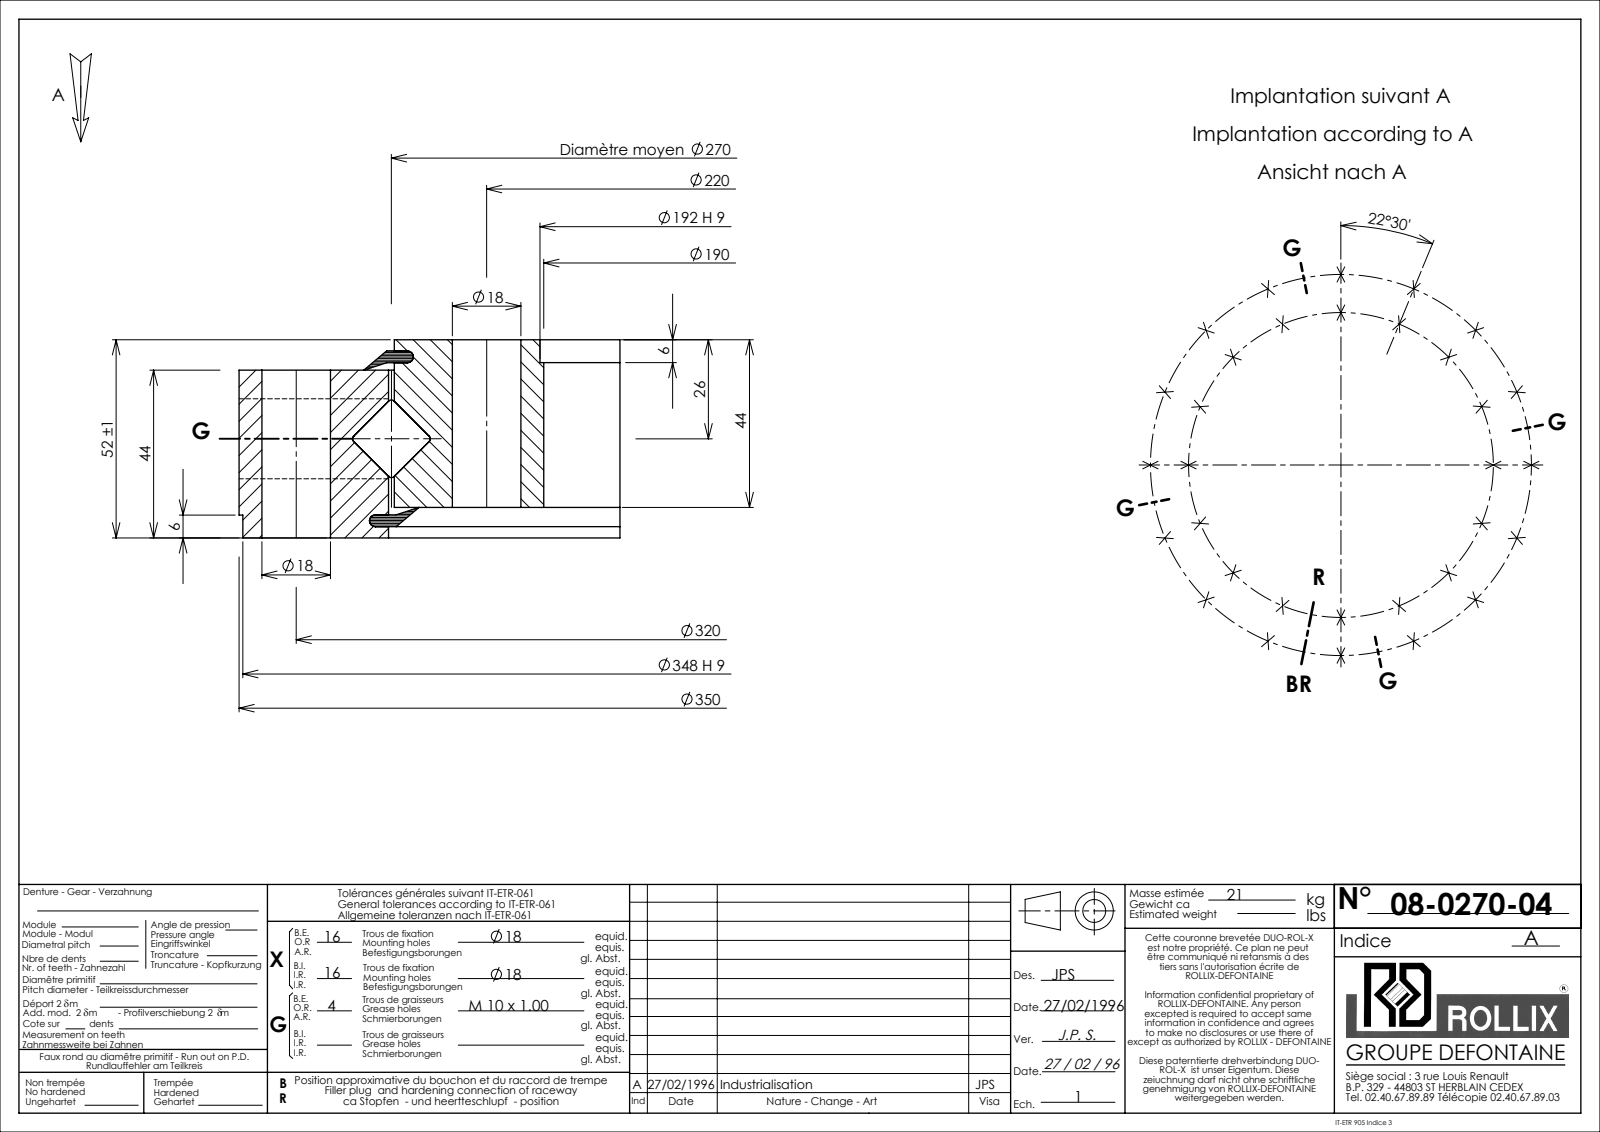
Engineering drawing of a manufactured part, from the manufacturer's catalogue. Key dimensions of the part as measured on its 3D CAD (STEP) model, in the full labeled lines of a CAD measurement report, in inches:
Part name (STEP PRODUCT): 08-0270-04
STEP written by: SolidWorks 2016 (CONFIG_CONTROL_DESIGN)
Units: inches
Bodies: 5 solids, 151 faces (16 planar, 94 cylindrical, 41 other)
Overall size (bounding box): 13.78 × 13.78 × 2.047
Volume: 147.6 in³ · Surface area: 664.1 in²
Round holes (diameter × count): ⌀0.709 ×32, ⌀0.354 ×4, ⌀7.48 ×1, ⌀7.559 ×1, ⌀10.689 ×1
Round bosses / shafts (diameter × count): ⌀13.78 ×1, ⌀13.701 ×1, ⌀10.571 ×1, ⌀0.591 ×1
Main face-to-face distances: 1.732, 0.315, 1.417, 2.047, 0.116, 1.931, 0.199, 1.616, 0.238, 1.809
Hole centre spacings: 2.833, 4.456, 8.906, 6.128, 7.644, 9.85, 2.458, 4.821
